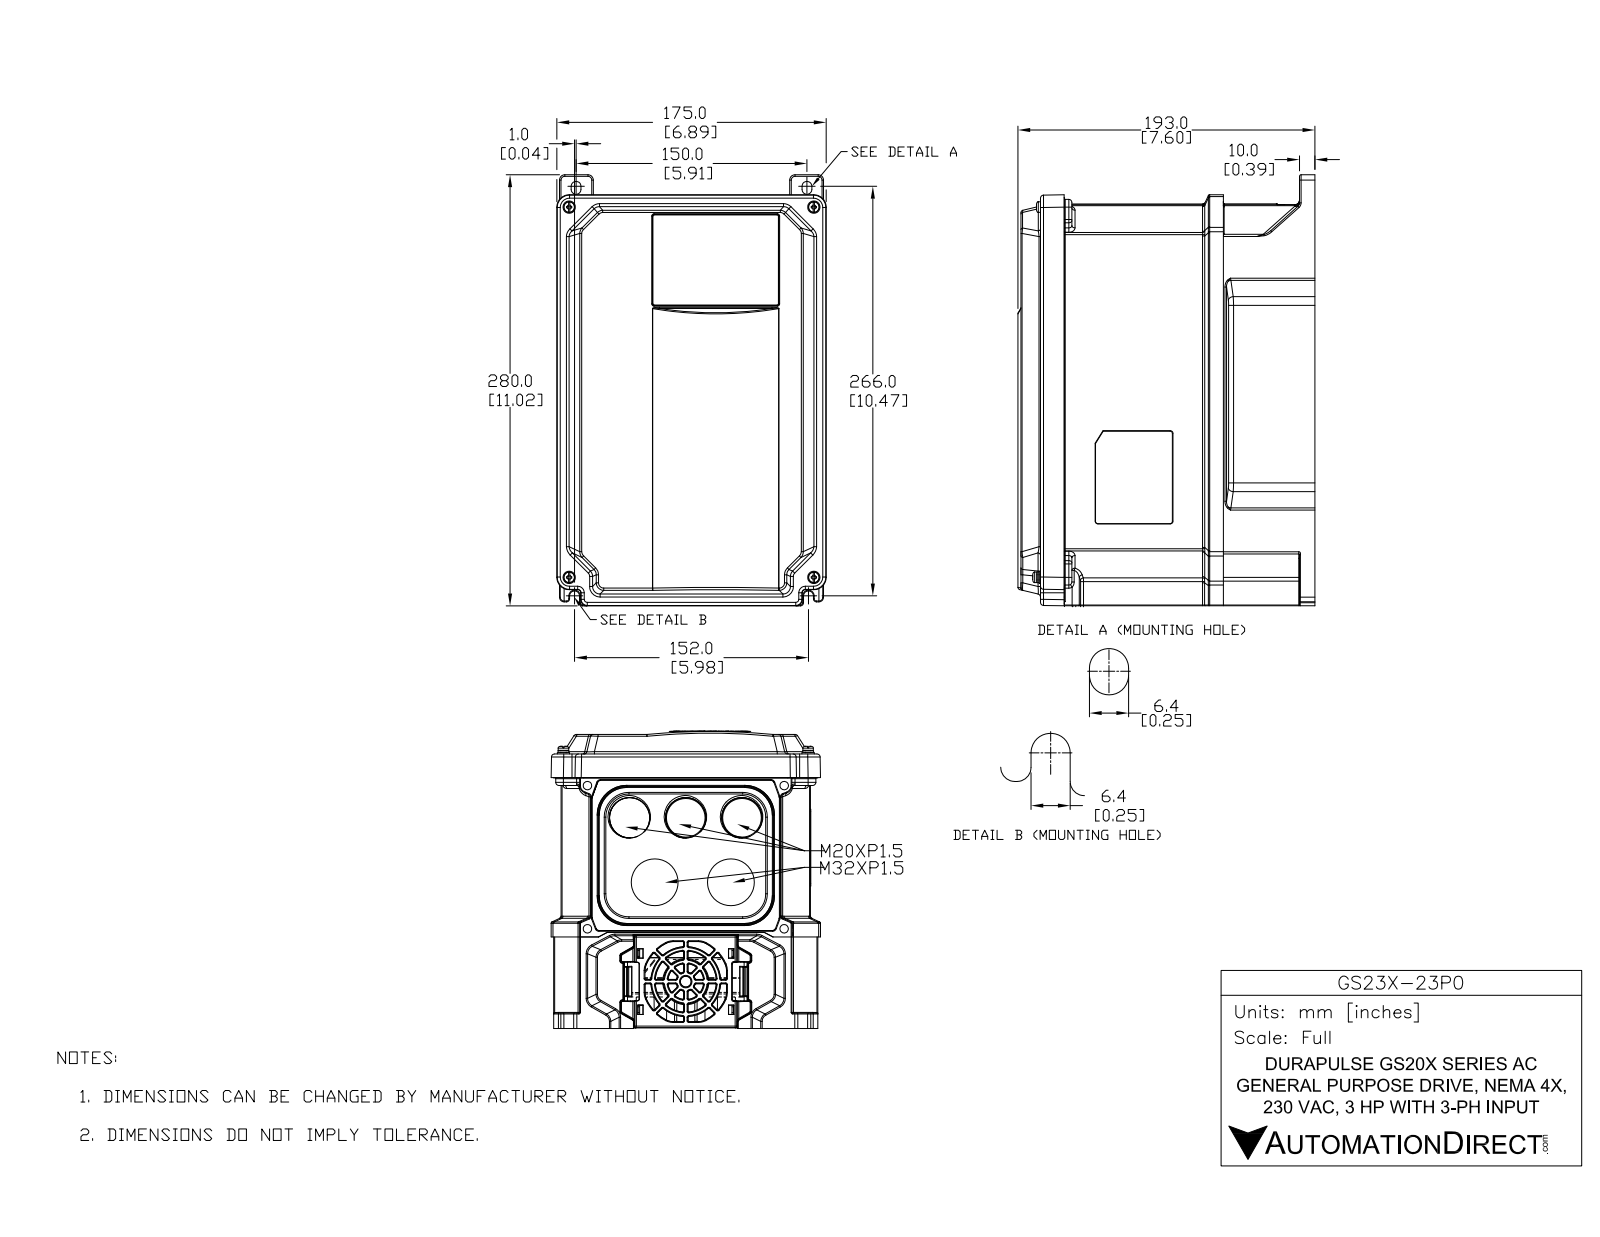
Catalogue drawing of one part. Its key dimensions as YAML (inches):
part_name: "GS21X-23P0"
step_written_by: "SolidWorks 2017 (AUTOMOTIVE_DESIGN)"
units: inches
bodies: {solids: 8, faces: 5100, planar: 1896, cylindrical: 1507, other: 1697}
overall_size: [11.024, 7.661, 6.895]
round_holes:
  - {diameter: 0.118, count: 4}
  - {diameter: 0.138, count: 4}
  - {diameter: 0.157, count: 2}
  - {diameter: 0.302, count: 1}
  - {diameter: 2.205, count: 1}
round_bosses_or_shafts:
  - {diameter: 0.217, count: 8}
  - {diameter: 0.724, count: 3}
  - {diameter: 1.197, count: 2}
  - {diameter: 1.181, count: 1}
  - {diameter: 0.341, count: 1}
partial_cylinders:
  - {radius: 0.02, count: 405}
  - {radius: 0.039, count: 188}
  - {radius: 0.012, count: 185}
  - {radius: 0.079, count: 104}
  - {radius: 0.197, count: 68}
  - {radius: 0.059, count: 50}
  - {radius: 0.157, count: 32}
  - {radius: 0.008, count: 28}
face_to_face_distances: [0.039, 7.48, 0.112, 7.368, 0.065, 6.378, 7.407, 6.313, 7.52, 0.138]
hole_center_spacings: [1.392, 1.969, 2.784, 6.26, 9.469, 11.351, 2.568, 2.835]
